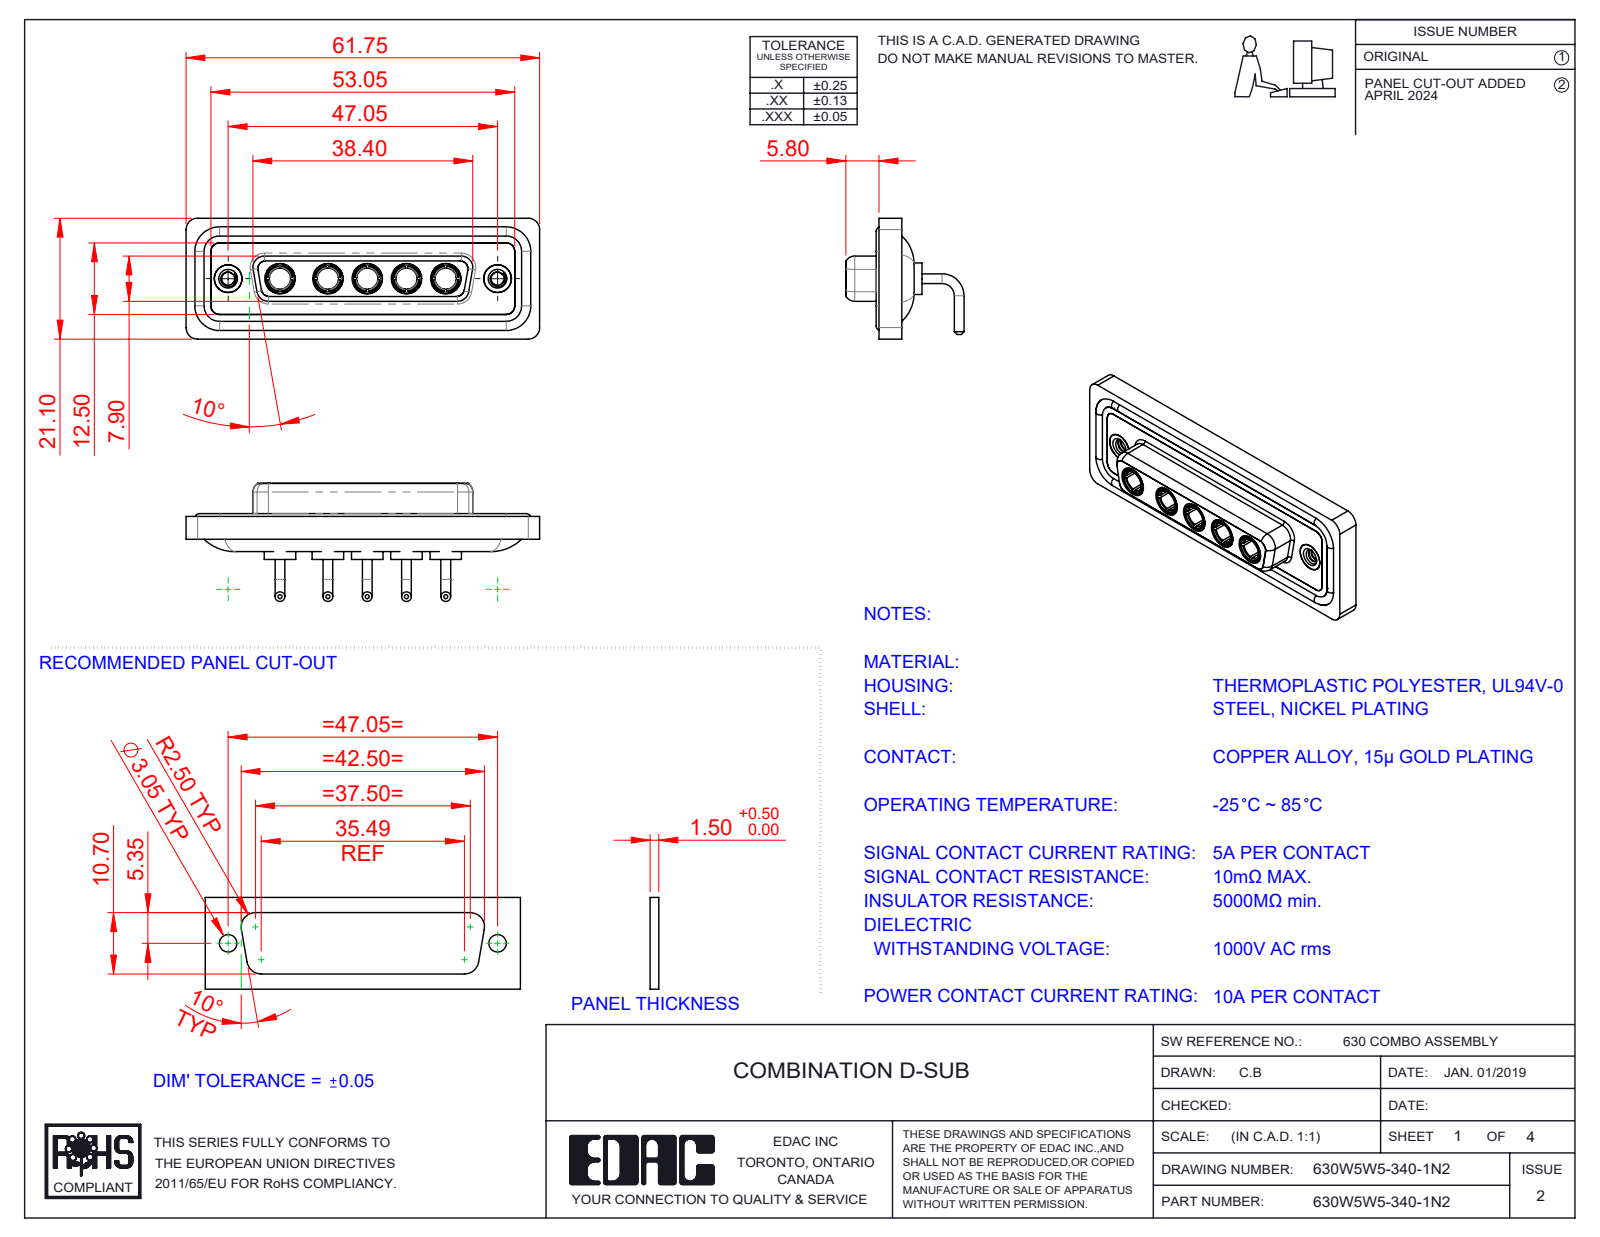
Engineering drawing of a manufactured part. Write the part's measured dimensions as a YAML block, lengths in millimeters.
part_name: "630Combo Threaded Rivet_2; 630Combo Shell Rear_25 Contacts; 630Combo Waterproof Housing_25 Contacts; Power Socket_10A RA (+3 more)"
step_written_by: "SolidWorks 2023 (CONFIG_CONTROL_DESIGN)"
units: millimeters
bodies: {solids: 17, faces: 776, planar: 250, cylindrical: 313, other: 213}
overall_size: [61.75, 21.1, 20.65]
volume: 8146
surface_area: 13559
round_holes:
  - {diameter: 4.85, count: 7}
  - {diameter: 3.7, count: 5}
  - {diameter: 5.3, count: 5}
  - {diameter: 2.26, count: 2}
  - {diameter: 4, count: 2}
  - {diameter: 4.05, count: 2}
  - {diameter: 5, count: 2}
round_bosses_or_shafts:
  - {diameter: 1.7, count: 10}
  - {diameter: 5.5, count: 5}
  - {diameter: 5.2, count: 5}
  - {diameter: 4.96, count: 5}
  - {diameter: 4.75, count: 5}
  - {diameter: 3.75, count: 5}
  - {diameter: 1.6, count: 4}
  - {diameter: 4.95, count: 2}
partial_cylinders:
  - {radius: 1.5, count: 18}
  - {radius: 2, count: 18}
  - {radius: 1.35, count: 8}
  - {radius: 1.6, count: 8}
  - {radius: 2.1, count: 5}
  - {radius: 0.25, count: 4}
  - {radius: 0.5, count: 4}
  - {radius: 0.6, count: 4}
face_to_face_distances: [0.4, 1.8, 4.1, 1.1, 1.5, 2.5, 3.1, 3.7, 1.6, 1.35]
hole_center_spacings: [6.86, 9.04, 38.01, 6.87, 8.38, 13.72, 13.73, 15.25]
